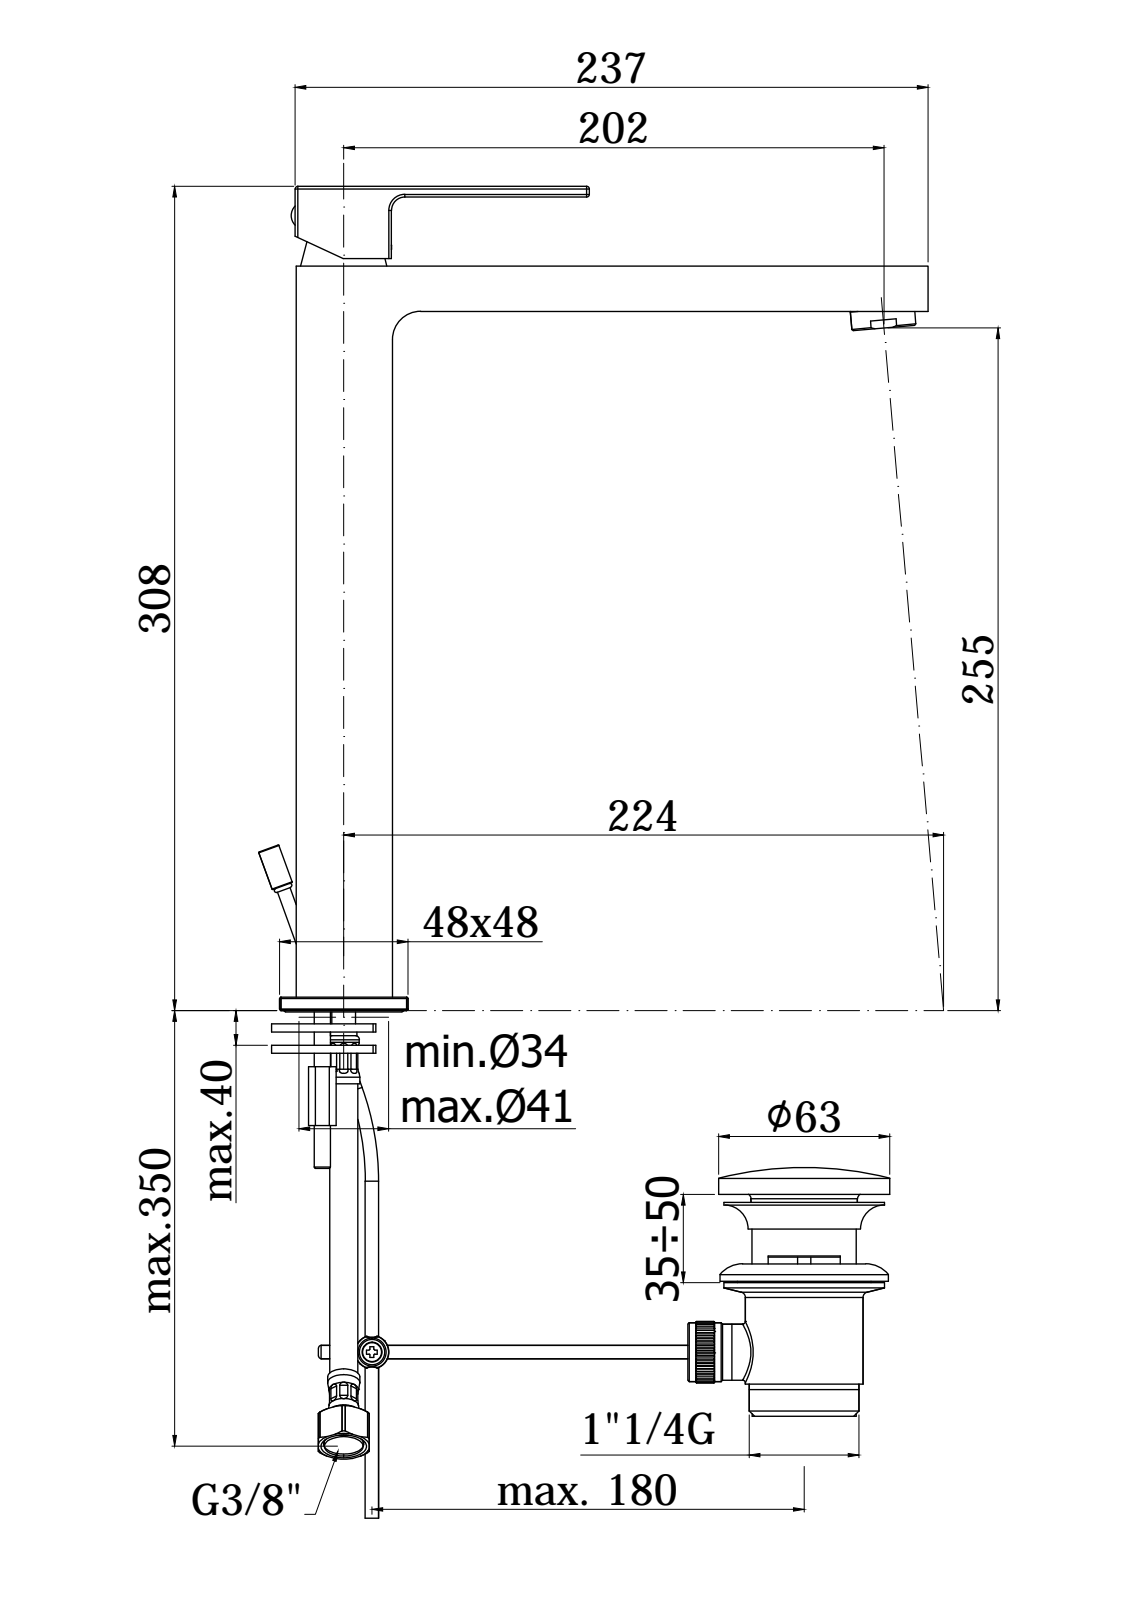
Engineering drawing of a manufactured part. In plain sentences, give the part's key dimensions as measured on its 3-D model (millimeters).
The part is named "EL085CR". Its 3-D file was written by "CREO PARAMETRIC BY PTC INC, 2020044 (CONFIG_CONTROL_DESIGN)". It is 2 solids with 160 faces: 57 planar, 61 cylindrical and 42 other. Overall it measures 306.78 by 252.56 by 48 millimeters. Its volume is 520 065 cubic millimeters and its surface area 83 985 square millimeters. Round holes: 1 of diameter 3, 1 of diameter 4.5, 1 of diameter 5.5, 1 of diameter 24.8, 1 of diameter 26.2, 1 of diameter 28. Round bosses or shafts: 1 of diameter 24, 1 of diameter 8, 1 of diameter 4. Partial cylindrical surfaces (rounded edges, fillets, slot ends): 13 of radius 1, 12 of radius 0.5, 8 of radius 1.5, 1 of radius 5, 1 of radius 10.5. The main face-to-face distances are 36, 17, 45.28, 28.28, 41.28, 24.28, 4, 261.5, 278.5, 302.78.
